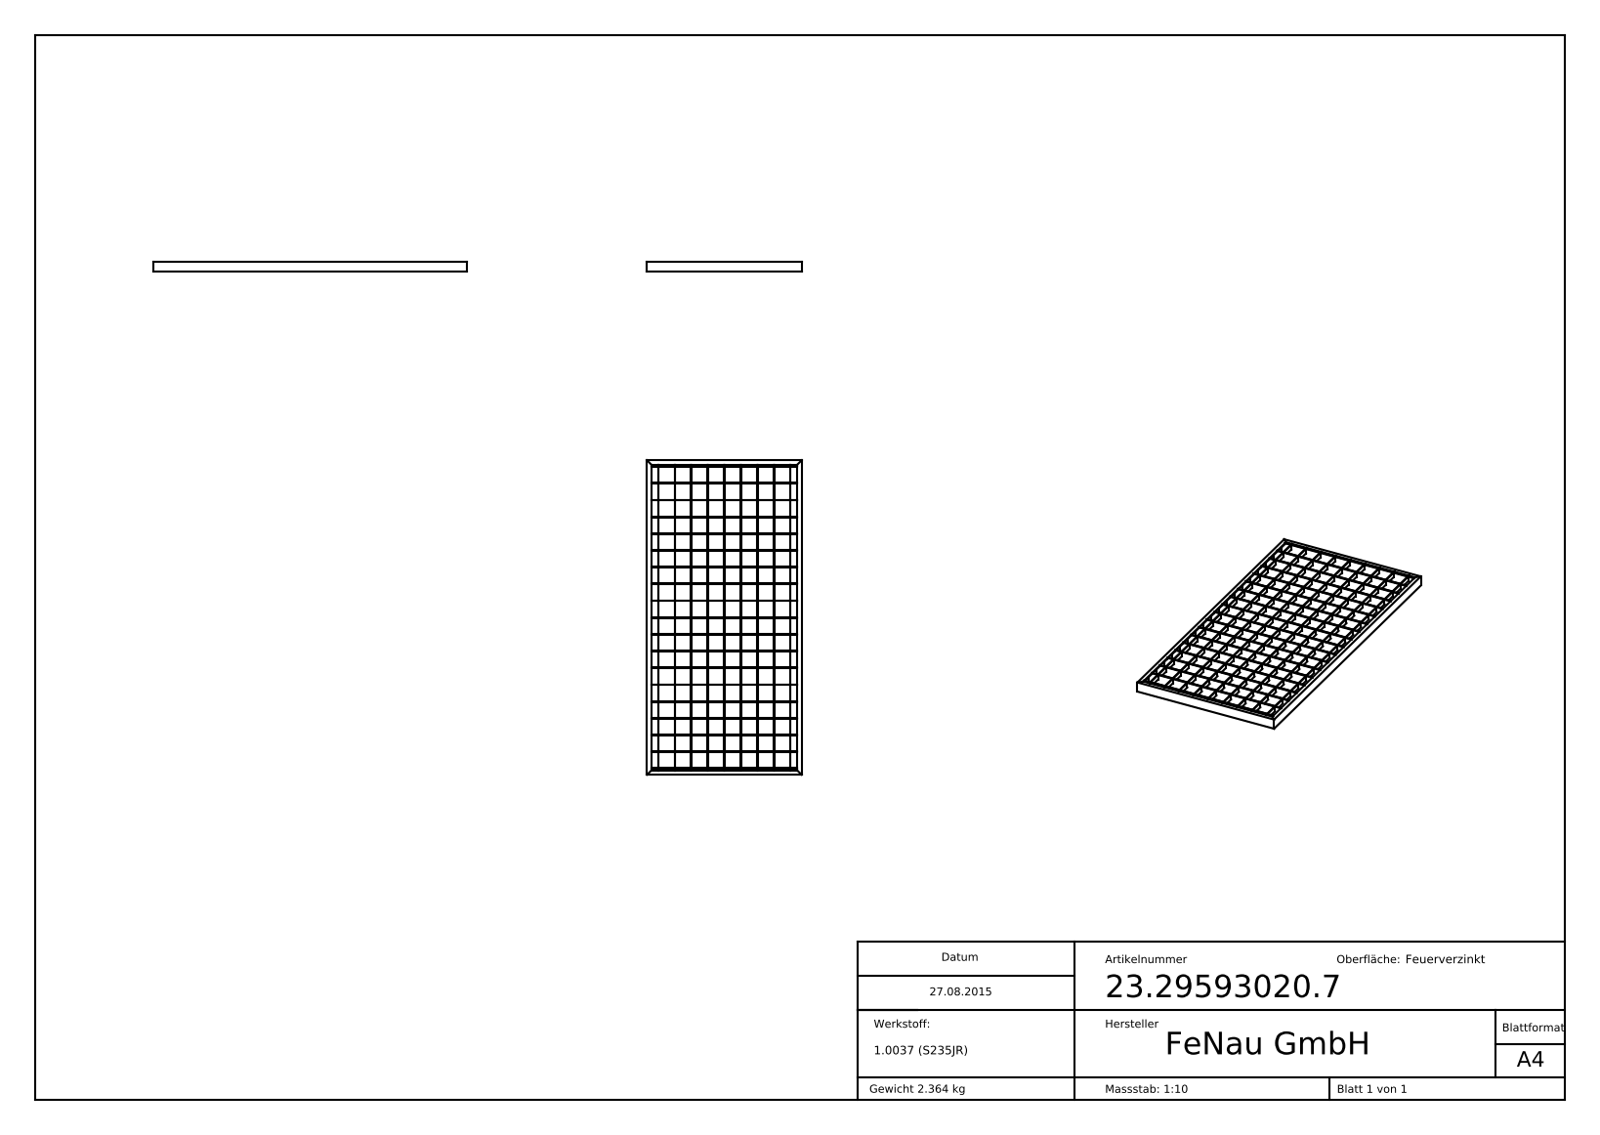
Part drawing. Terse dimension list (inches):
name: 23-29593020-7
written by: SolidWorks 2015 (CONFIG_CONTROL_DESIGN)
unit: in
bodies: 1 solid, 748 faces (748 planar, 0 cylindrical, 0 other)
size: 23.228 × 11.417 × 0.787
volume: 18.49 in³; area: 673.8 in²
face distances: 2.48, 1.24, 3.72, 4.961, 1.22, 6.201, 7.441, 2.441, 8.681, 9.921
